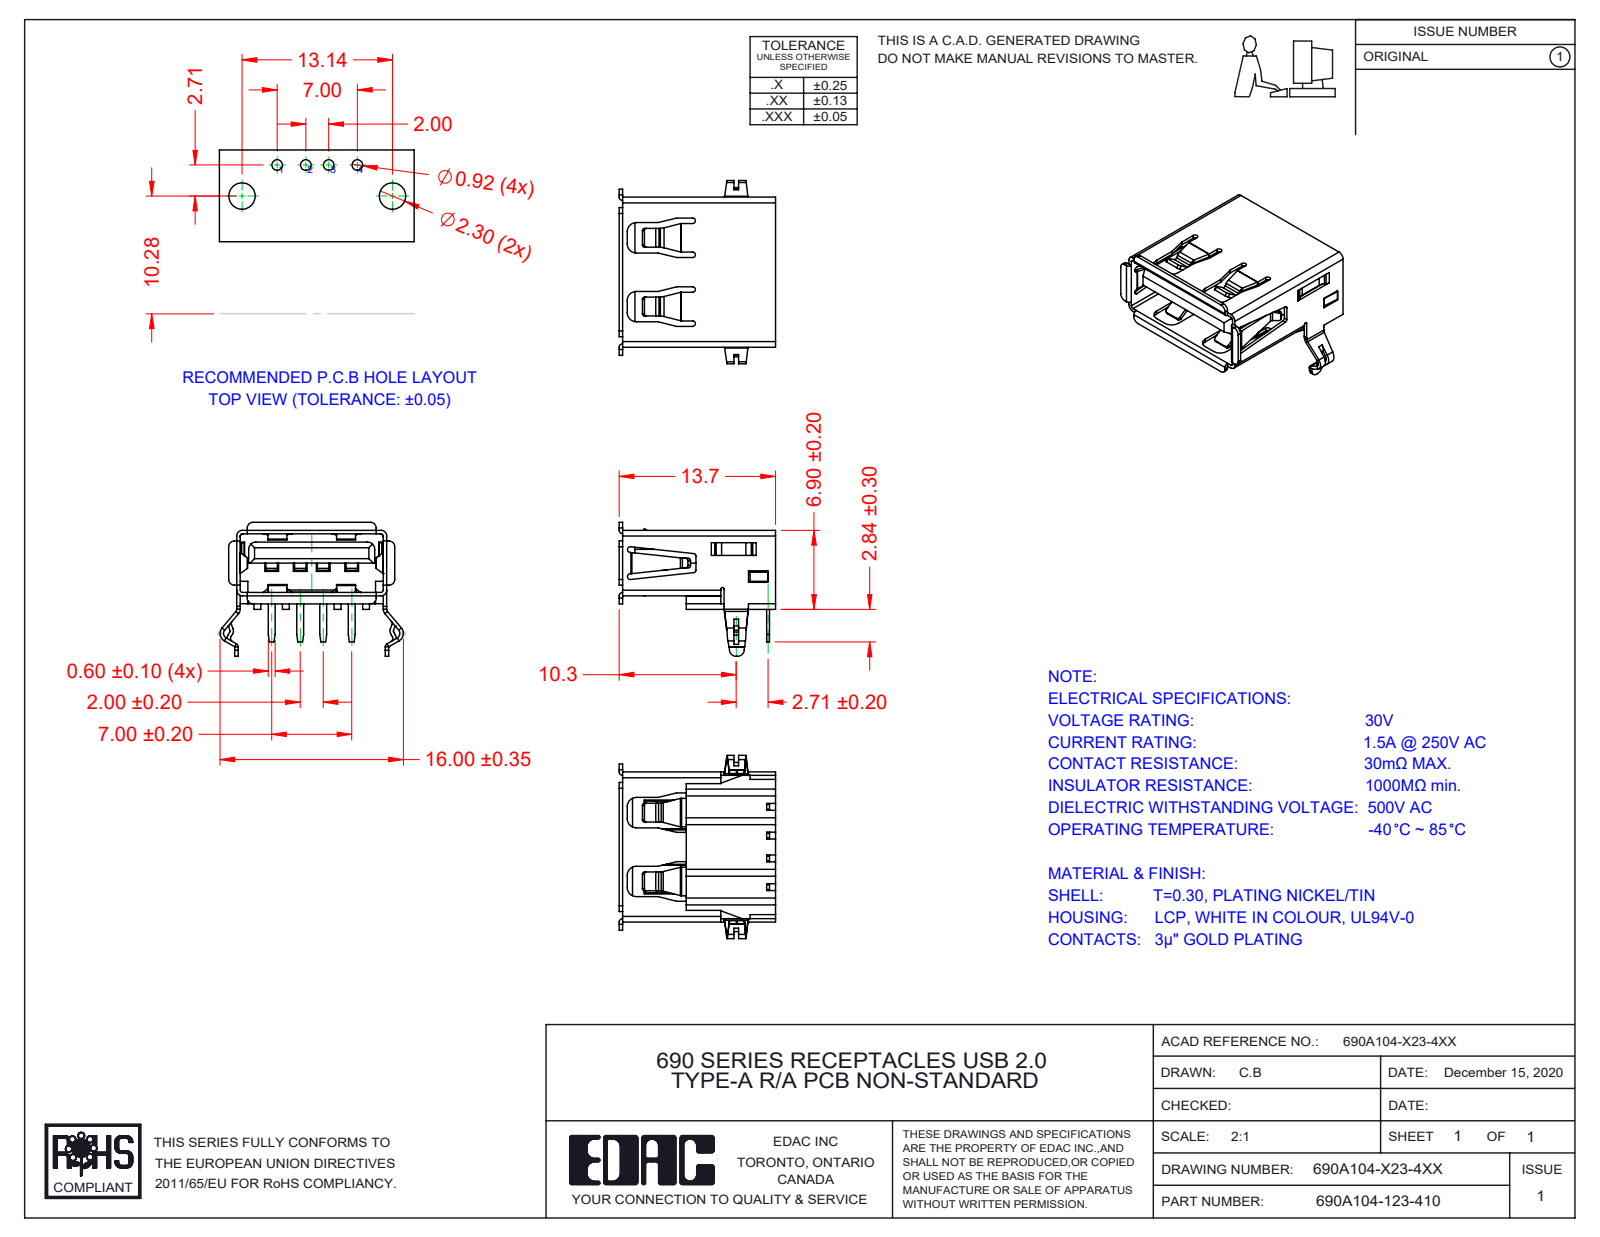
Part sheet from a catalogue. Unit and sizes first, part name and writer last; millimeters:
Units: millimetres
Overall size (bounding box): 16 × 13.65 × 11.7
Partial cylindrical surfaces — rounded edges, fillets, slot ends (radius × count): R0.2 ×30, R0.5 ×24, R0.3 ×12, R0.1 ×10, R0.6 ×8, R0.8 ×8, R0.25 ×6, R0.24 ×4
Main face-to-face distances: 5.42, 2.86, 2.56, 12.8, 1.27, 4.15, 1.02, 5.12, 5.72, 1.57
Volume: 557 mm³ · Surface area: 2 007 mm²
Bodies: 6 solids, 826 faces (606 planar, 184 cylindrical, 36 other)
Part name (STEP PRODUCT): Shell 690A104-X23-4XX; Insulator 690A104-X23-4XX_White; 690A104-123-410; Contact 690A104-X23-4XX
STEP written by: SolidWorks 2020 (AUTOMOTIVE_DESIGN)
